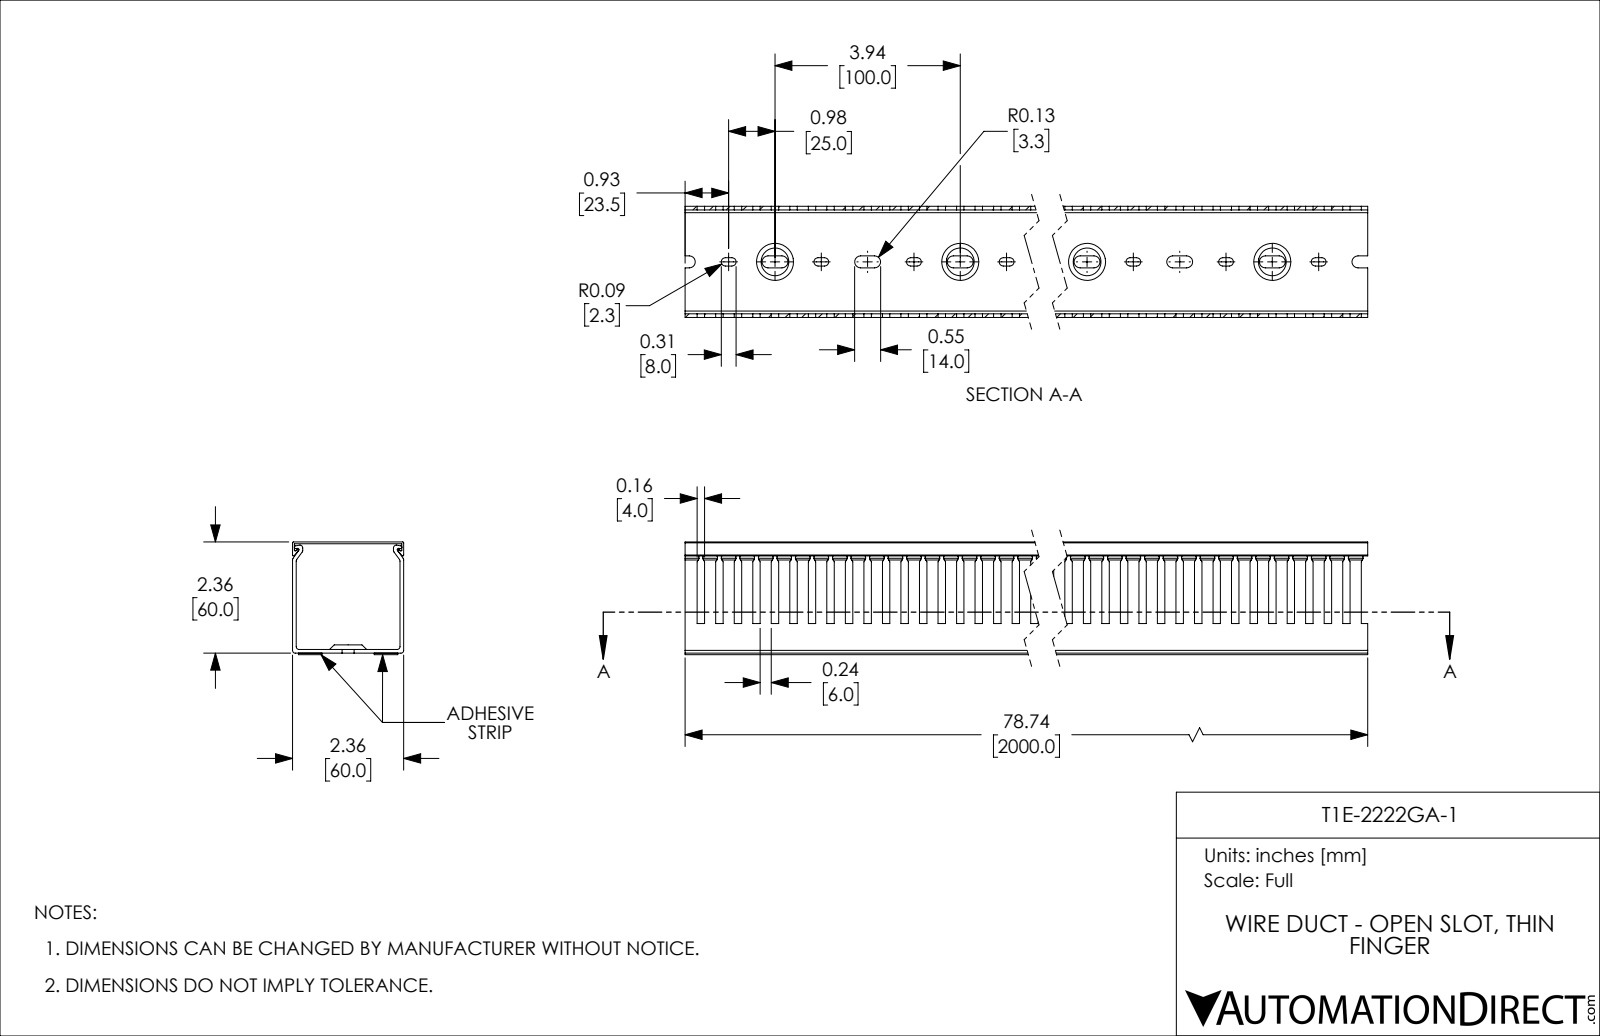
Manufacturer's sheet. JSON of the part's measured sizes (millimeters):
{"part_name": "T1E-2222GA-1", "step_written_by": "SolidWorks 2021 (CONFIG_CONTROL_DESIGN)", "units": "millimeters", "bodies": {"solids": 4, "faces": 1017, "planar": 546, "cylindrical": 431, "other": 40}, "overall_size": [2000, 60.79, 60], "volume_mm3": 903063, "surface_area_mm2": 1127000, "partial_cylinders_radius": [[2.25, 80], [3.25, 80], [1.5, 12], [0.5, 8], [0.75, 6]], "face_to_face_distances": [2, 58, 60, 1, 59, 57, 56, 0.79, 2.79, 59.79]}
